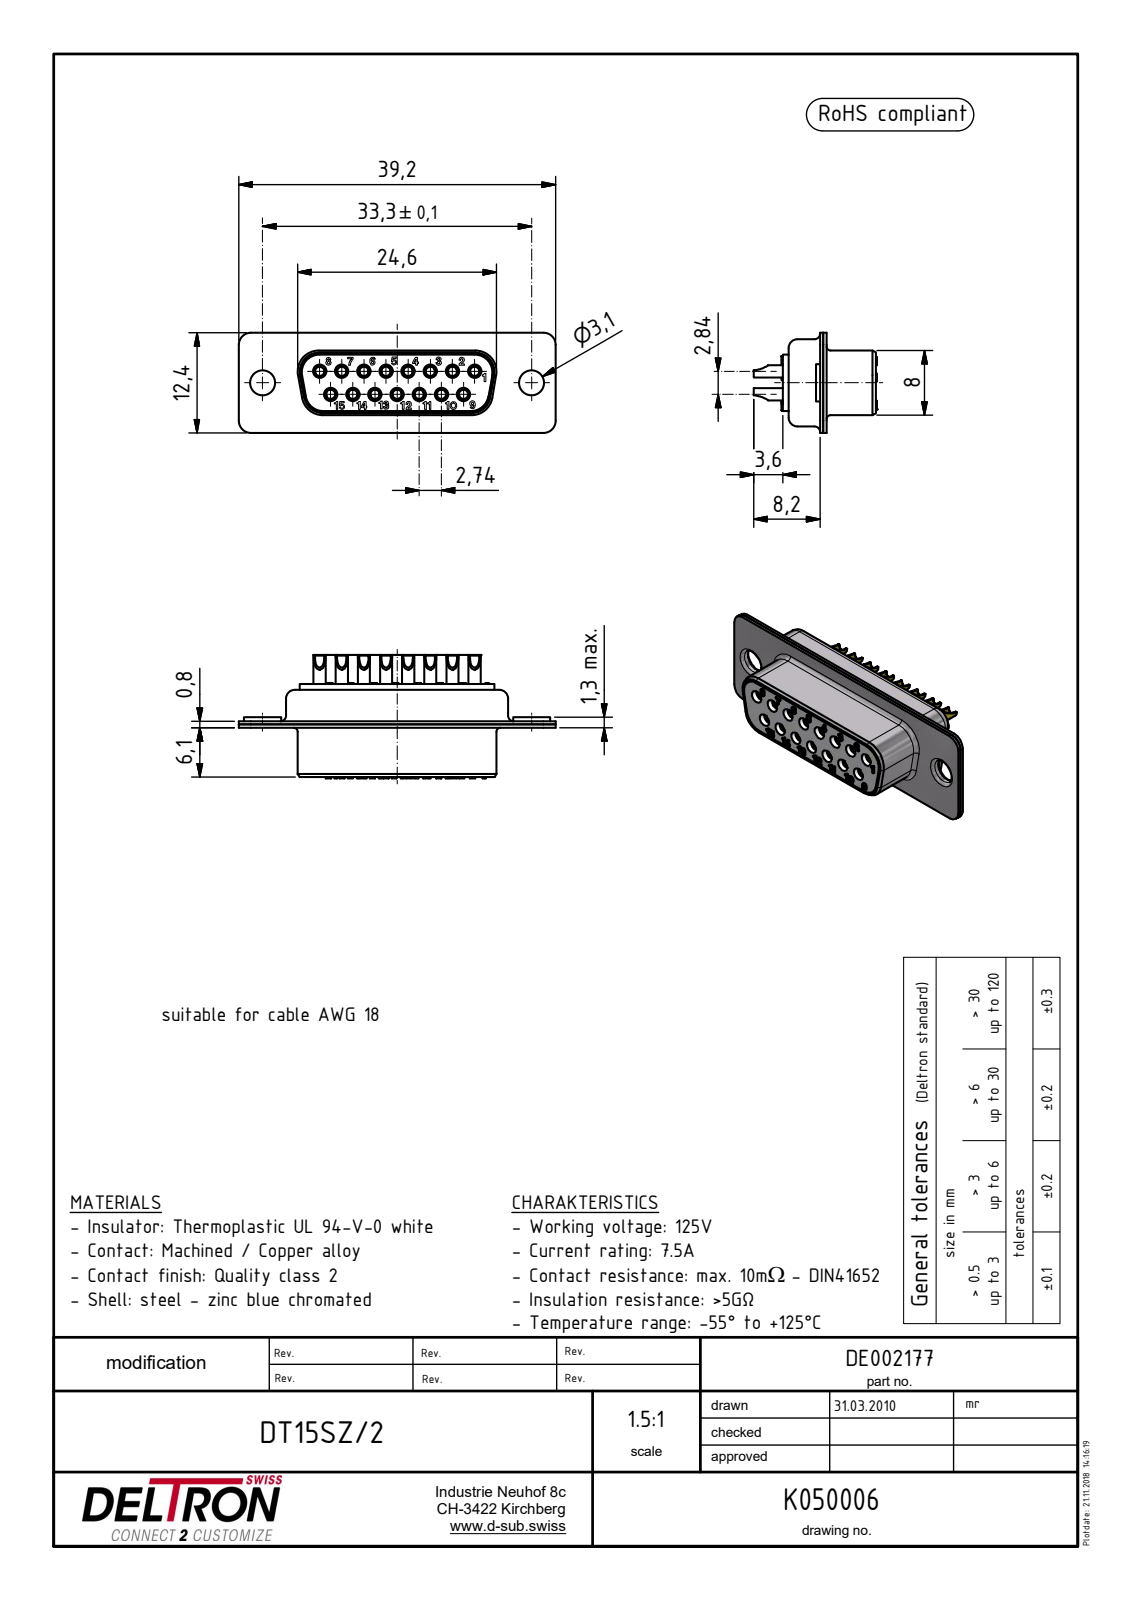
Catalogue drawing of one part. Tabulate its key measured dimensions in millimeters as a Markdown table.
| quantity | value |
| --- | --- |
| part name | N00404_BG; R+B00894_BG; R+B00153_BG; R+B00144_BG (+1 more) |
| STEP written by | Autodesk Inventor 2015 (AUTOMOTIVE_DESIGN) |
| units | millimeters |
| bodies | 18 solids, 1240 faces (634 planar, 329 cylindrical, 277 other) |
| overall size | 39.2 × 15.25 × 12.4 |
| volume | 2 350 mm³ |
| surface area | 6 335 mm² |
| round holes (diameter × count) | 1.15 × 15, 1.2 × 15, 1.92 × 15, 2.3 × 15, 0.34 × 4, 0.24 × 2, 0.28 × 2, 3.1 × 2, 4.06 × 2 |
| round bosses / shafts (diameter × count) | 2.23 × 15, 1.96 × 15, 1.7 × 15, 1.6 × 15, 1.5 × 15, 4.6 × 2, 3.9 × 2 |
| partial cylindrical surfaces (radius × count) | 0.25 × 16, 2 × 12, 0.7 × 8, 1.1 × 8, 2.2 × 8, 0.34 × 4, 0.5 × 4, 0.9 × 4 |
| main face-to-face distances | 0.4, 0.8, 1.4, 0.5, 10.2, 7.1, 7.6, 7.5, 1.3, 7 |
| hole center spacings | 3.15, 2.74, 5, 5.48, 7.42, 8.22, 10, 10.96 |
